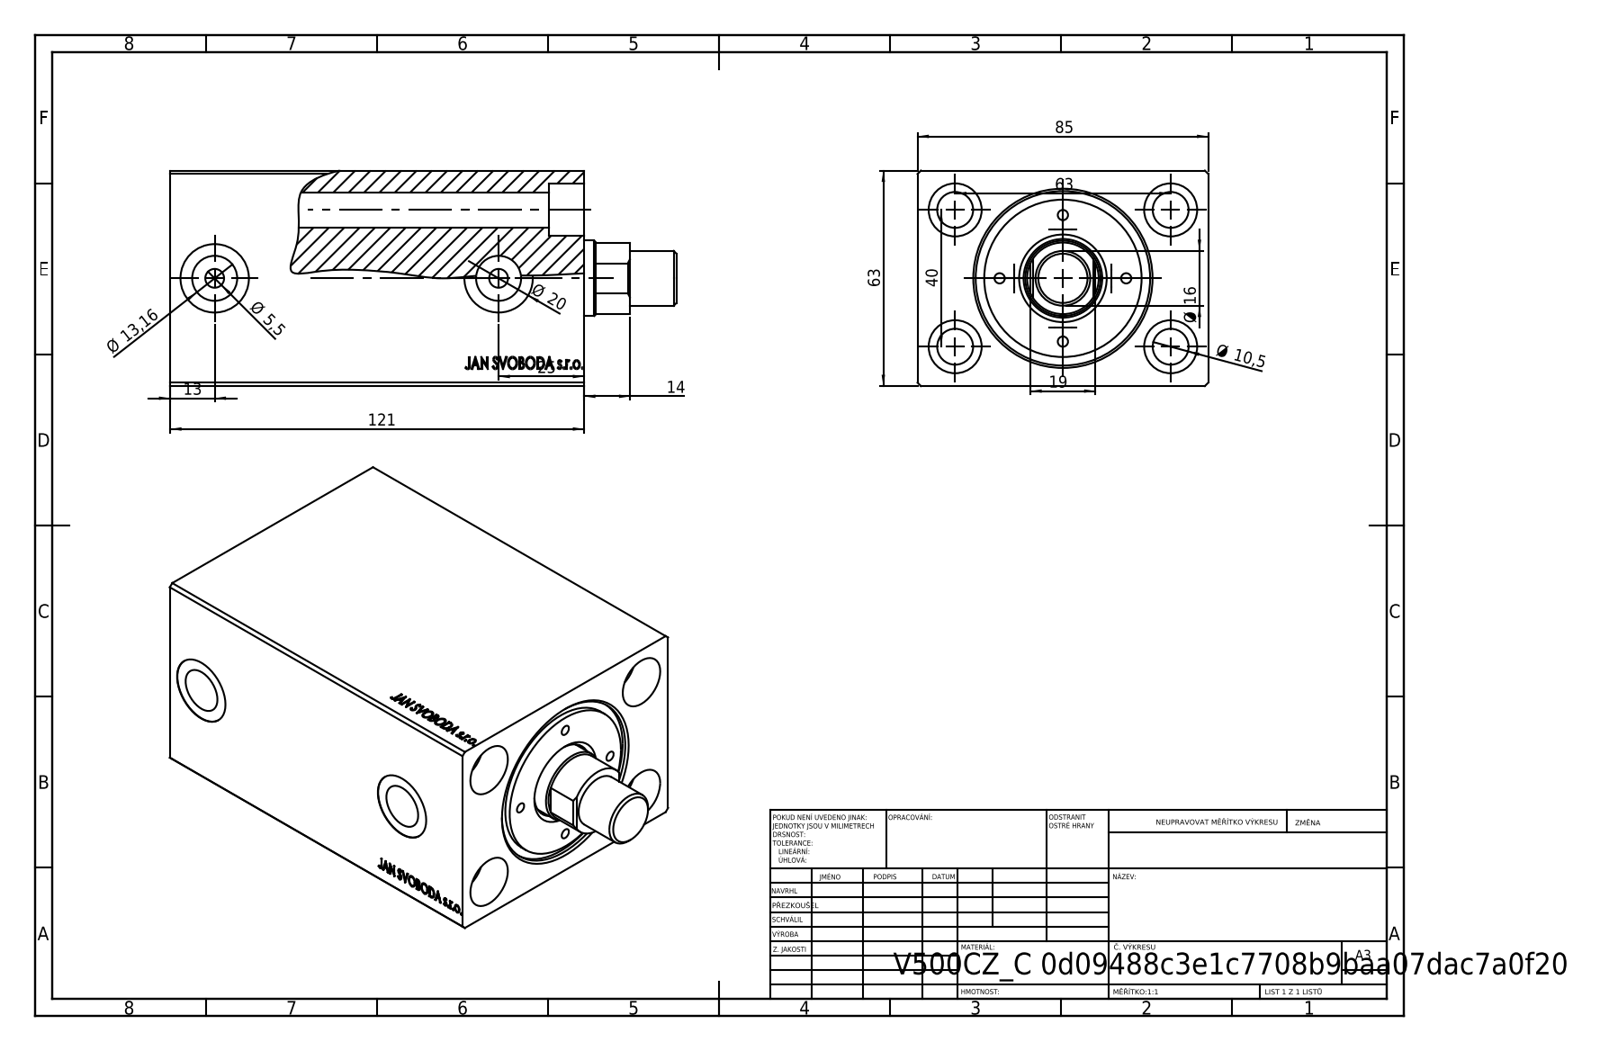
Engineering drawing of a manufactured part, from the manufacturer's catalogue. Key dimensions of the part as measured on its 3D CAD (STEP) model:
Part name (STEP PRODUCT): V500CZ_VCP_C; V500CZ_MALE_METRIC; V500CZ_C; V500CZ_VC_vysunovaci_C
STEP written by: SolidWorks 2019 (CONFIG_CONTROL_DESIGN)
Units: millimetres
Bodies: 4 solids, 884 faces (413 planar, 71 cylindrical, 400 other)
Overall size (bounding box): 148 × 85 × 63
Volume: 556 631 mm³ · Surface area: 94 875 mm²
Round holes (diameter × count): ⌀3 ×4, ⌀10.5 ×4, ⌀15.5 ×4, ⌀5.5 ×2, ⌀13.16 ×2, ⌀20 ×2, ⌀16 ×1, ⌀22 ×1, ⌀23 ×1, ⌀36 ×1, ⌀40 ×1, ⌀51 ×1
Round bosses / shafts (diameter × count): ⌀46 ×1, ⌀14 ×1
Partial cylindrical surfaces — rounded edges, fillets, slot ends (radius × count): R10.46 ×1
Main face-to-face distances: 63, 85, 121, 36, 11.8, 73.2, 109.2, 10, 1.8, 25
Hole centre spacings: 18.5, 23.85, 26.16, 31.54, 37.31, 49.74, 53.85, 37
